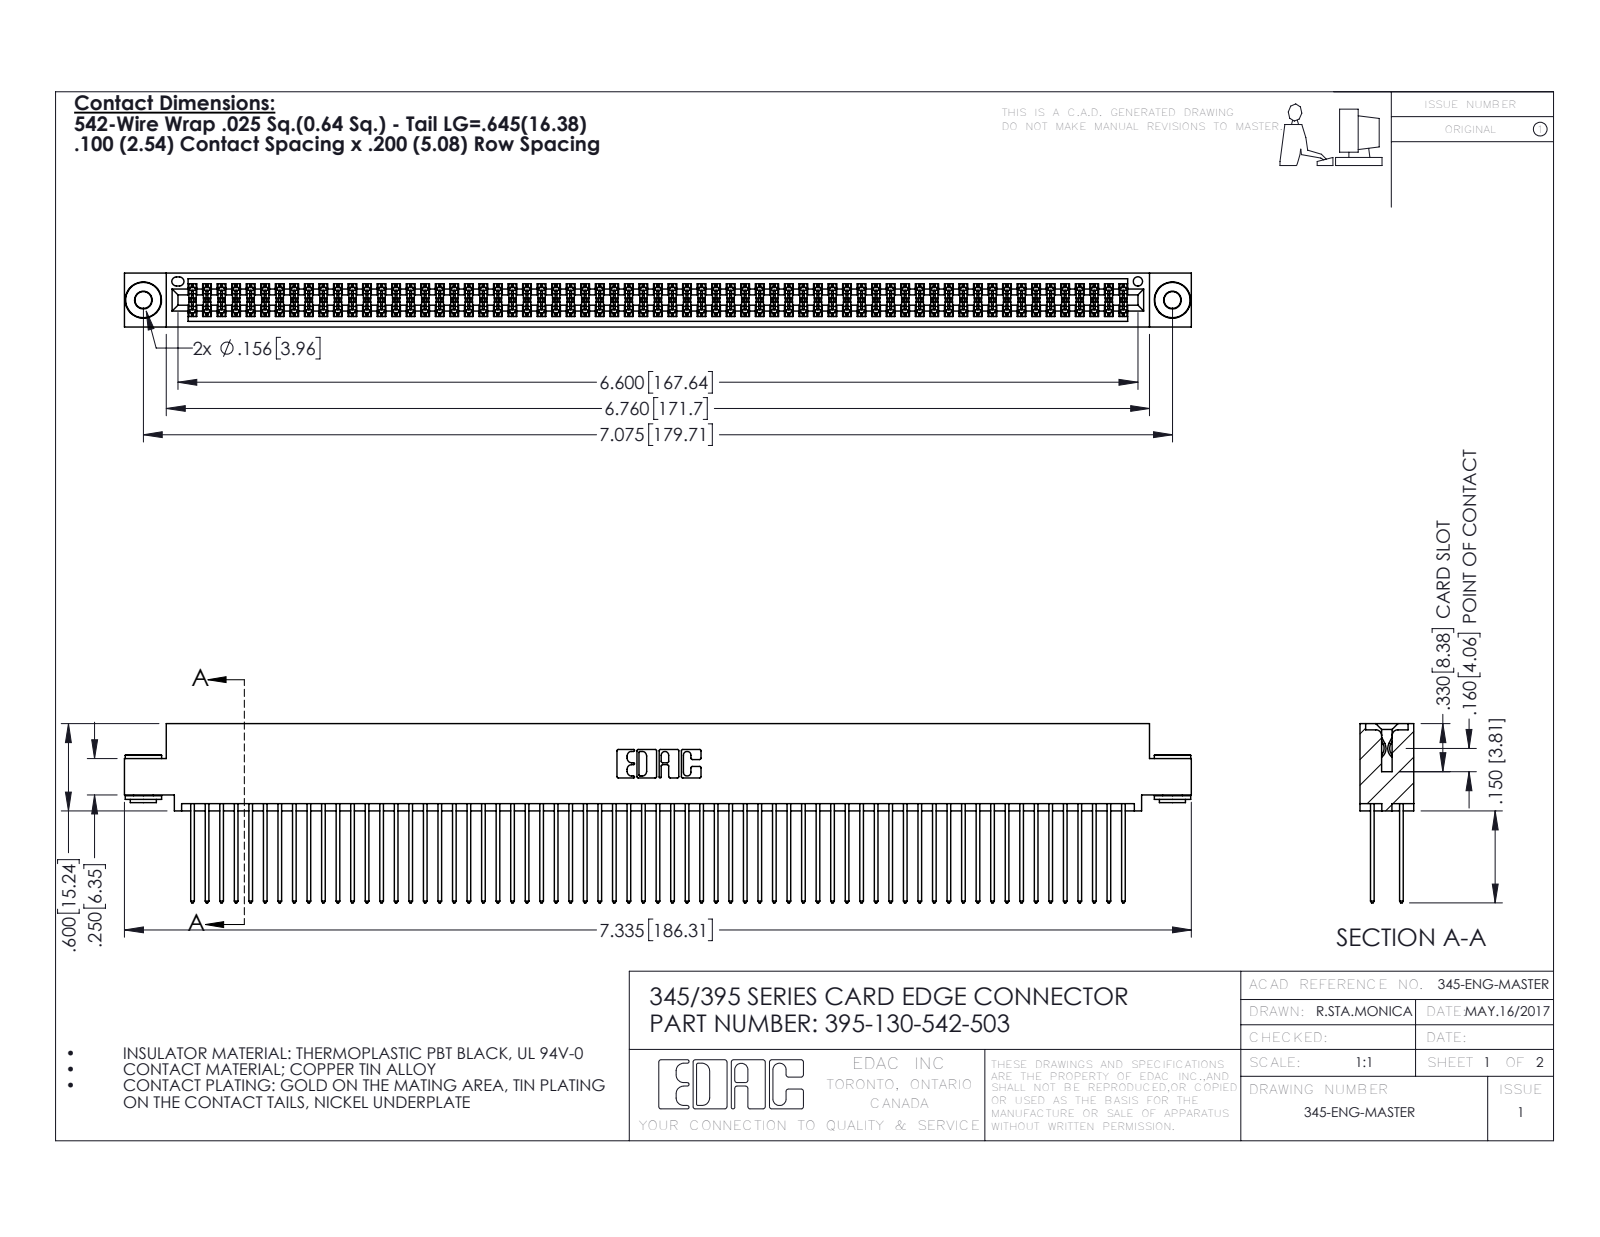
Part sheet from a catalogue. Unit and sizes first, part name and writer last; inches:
Units: inches
Overall size (bounding box): 7.335 × 1.232 × 0.37
Round holes (diameter × count): ⌀0.116 ×2, ⌀0.156 ×2, ⌀0.064 ×1
Round bosses / shafts (diameter × count): ⌀0.25 ×2, ⌀0.18 ×2, ⌀0.136 ×2
Partial cylindrical surfaces — rounded edges, fillets, slot ends (radius × count): R0.006 ×195, R0.01 ×130, R0.01 ×22, R0.007 ×6, R0.031 ×6, R0.026 ×3, R0.014 ×2, R0.019 ×2
Main face-to-face distances: 0.072, 0.298, 0.2, 0.025, 0.098, 0.272, 0.225, 0.37, 0.175, 0.149
Hole centre spacings: 0.27, 6.839, 7.075
Volume: 1.151 in³ · Surface area: 48.76 in²
Bodies: 133 solids, 6668 faces (4384 planar, 2276 cylindrical, 8 other)
Part name (STEP PRODUCT): 345 Part_0.110 Offset - 0.156 Dia-TH; 345-250-002_345-250-002-102; 345-292-001_345-293-142; 395-130-542-503
STEP written by: SolidWorks 2016 (CONFIG_CONTROL_DESIGN)
